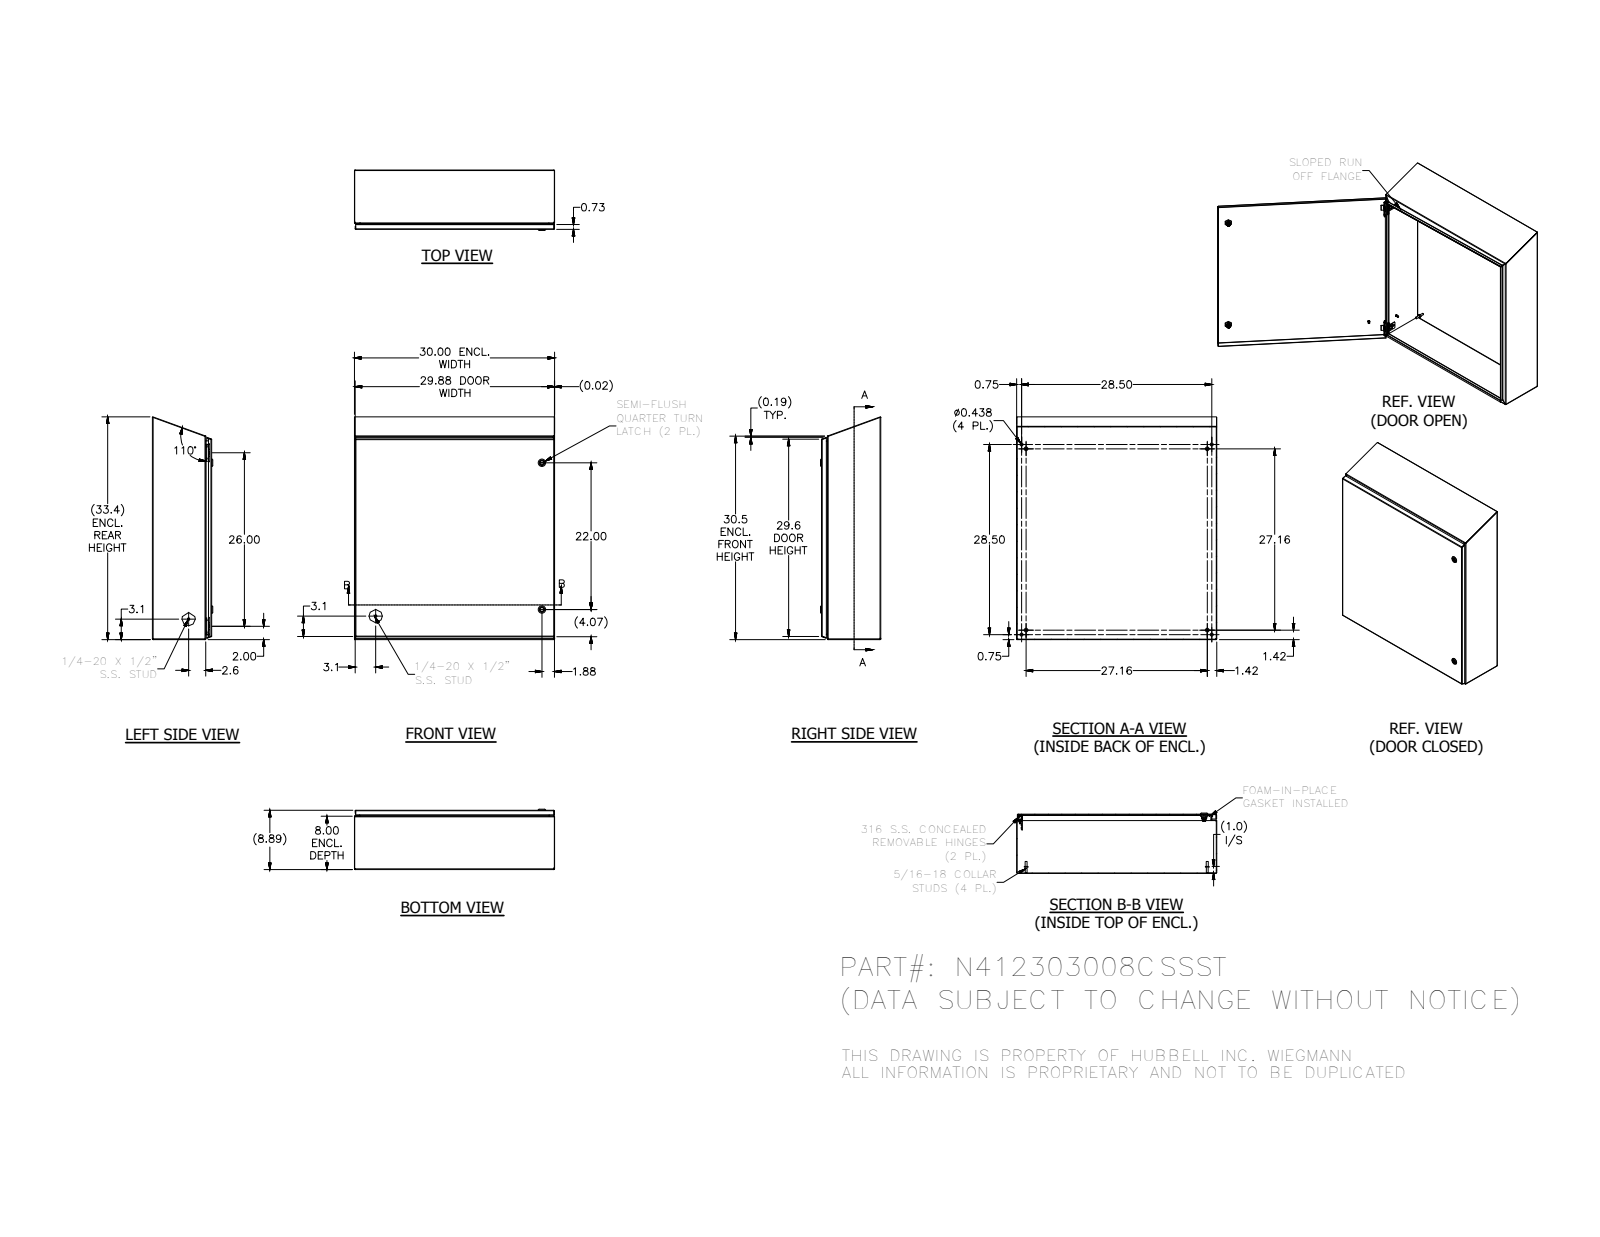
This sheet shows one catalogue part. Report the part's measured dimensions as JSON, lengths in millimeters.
{"part_name": "N412_CSSST-assm; N412303008CSSSTB3S; HFW3161; HFW328176 (+8 more)", "step_written_by": "Autodesk Inventor 2012 (AUTOMOTIVE_DESIGN)", "units": "millimeters", "bodies": {"solids": 42, "faces": 1732, "planar": 717, "cylindrical": 604, "other": 411}, "overall_size": [848.1, 762, 229.7], "volume_mm3": 3825000, "surface_area_mm2": 4093000, "round_holes": [[2.4, 4], [3.9, 4], [4.2, 4], [4.4, 4], [4.7, 4], [11.1, 4], [4, 3], [5, 2], [8, 2], [10, 2], [10.2, 2], [16.1, 2]], "round_bosses_or_shafts": [[6.4, 10], [14.3, 4], [9.1, 4], [8.1, 4], [7.6, 4], [7, 4], [6.5, 4], [4.2, 4]], "partial_cylinders_radius": [[0.8, 29], [1.3, 26], [0.5, 24], [2.7, 19], [0.4, 18], [3.2, 16], [0.8, 8], [4.5, 6]], "face_to_face_distances": [1.9, 223.9, 225.7, 222, 760.1, 762, 758.2, 201.3, 22.5, 20.7], "hole_center_spacings": [660.4, 723.9, 731.2, 12.7, 16.7, 16.8, 24.2, 33.2]}
